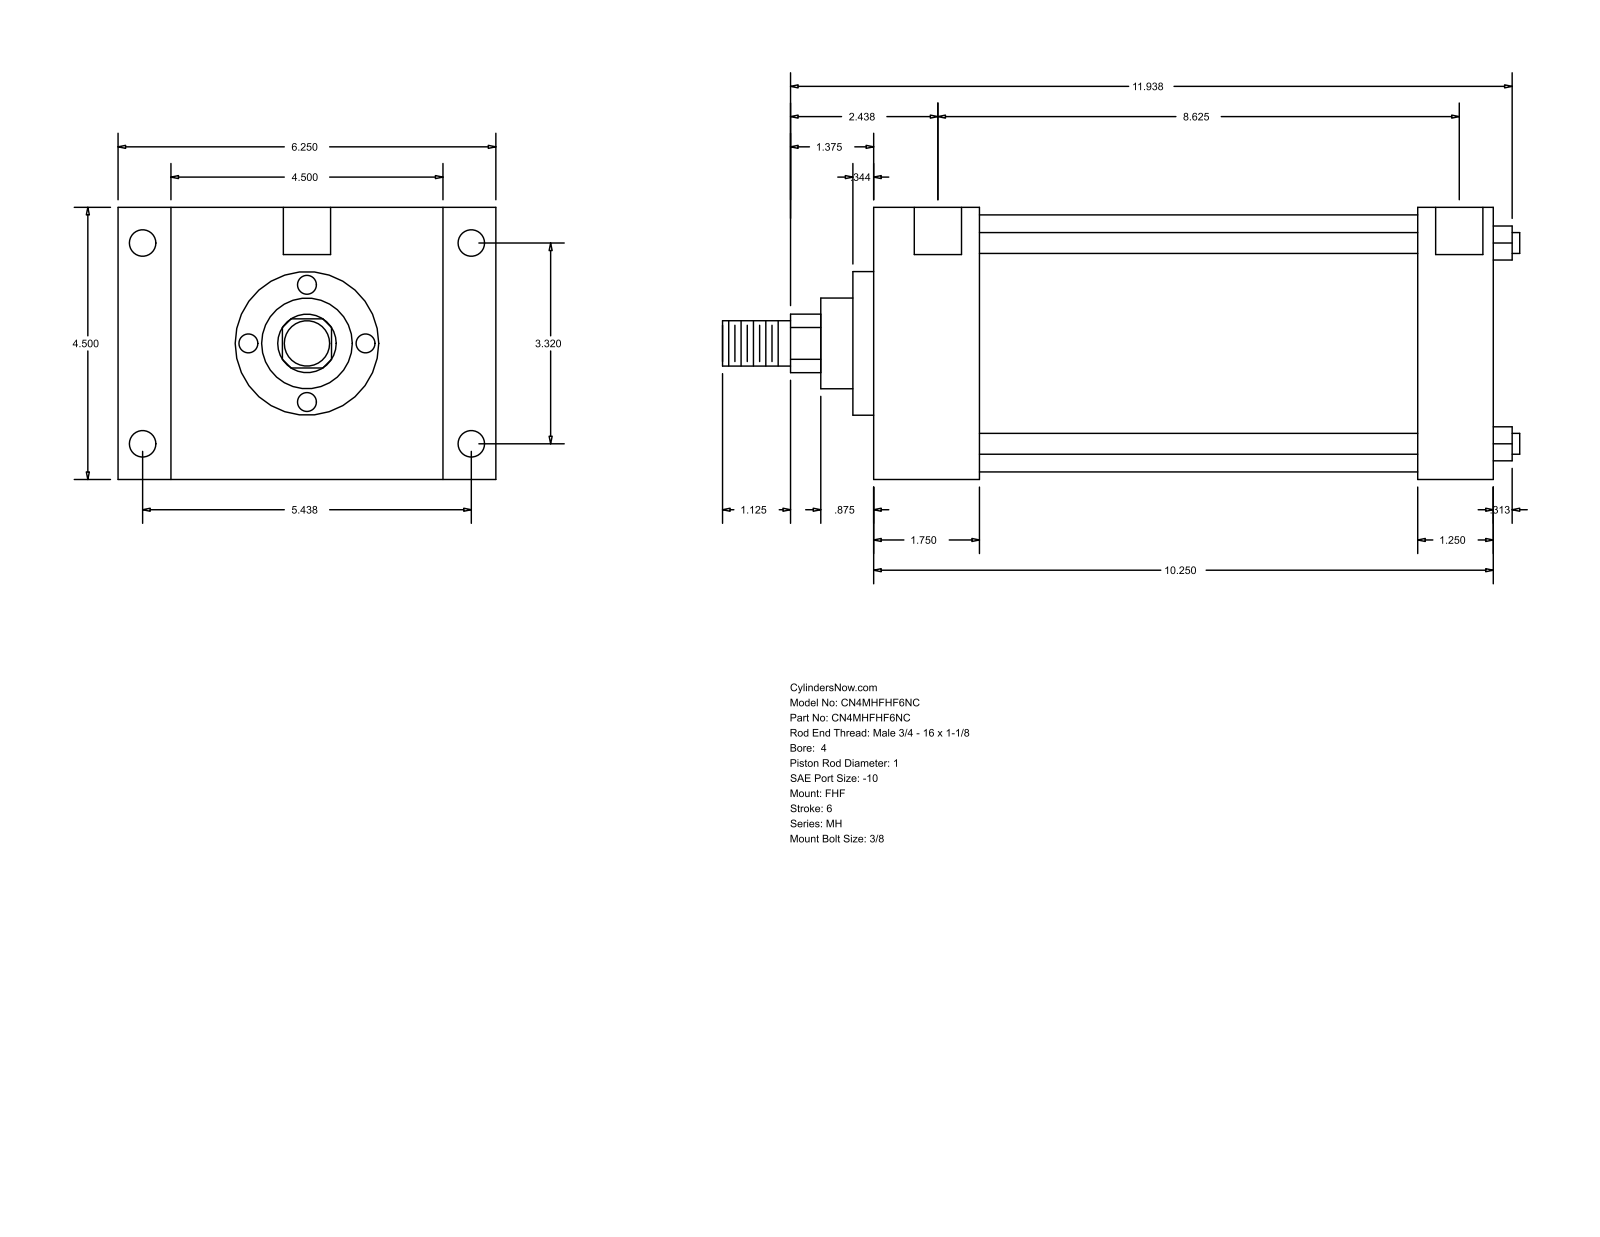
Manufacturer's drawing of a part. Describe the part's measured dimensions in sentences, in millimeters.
The part is named "MH_FHF__0400_1". Its 3-D file was written by "GSSL Pune (CONFIG_CONTROL_DESIGN)". It is 0 solids with 90 faces: 61 planar, 29 cylindrical and 0 other. Overall it measures 334.96 by 158.75 by 114.3 millimeters. Round holes: 4 of diameter 8.73, 4 of diameter 11.13, 2 of diameter 19.84. Round bosses or shafts: 4 of diameter 8.76, 1 of diameter 107.95, 1 of diameter 60.33, 1 of diameter 38.1, 1 of diameter 25.4, 1 of diameter 19.05. Partial cylindrical surfaces (rounded edges, fillets, slot ends): 1 of radius 12.29. The main face-to-face distances are 114.3, 260.35, 44.46, 215.89, 22.23, 136.53, 158.76, 228.6, 184.14, 31.75. The hole center spacings are 1.58, 84.32, 138.12, 161.82, 220.66, 222.24, 219.08.
